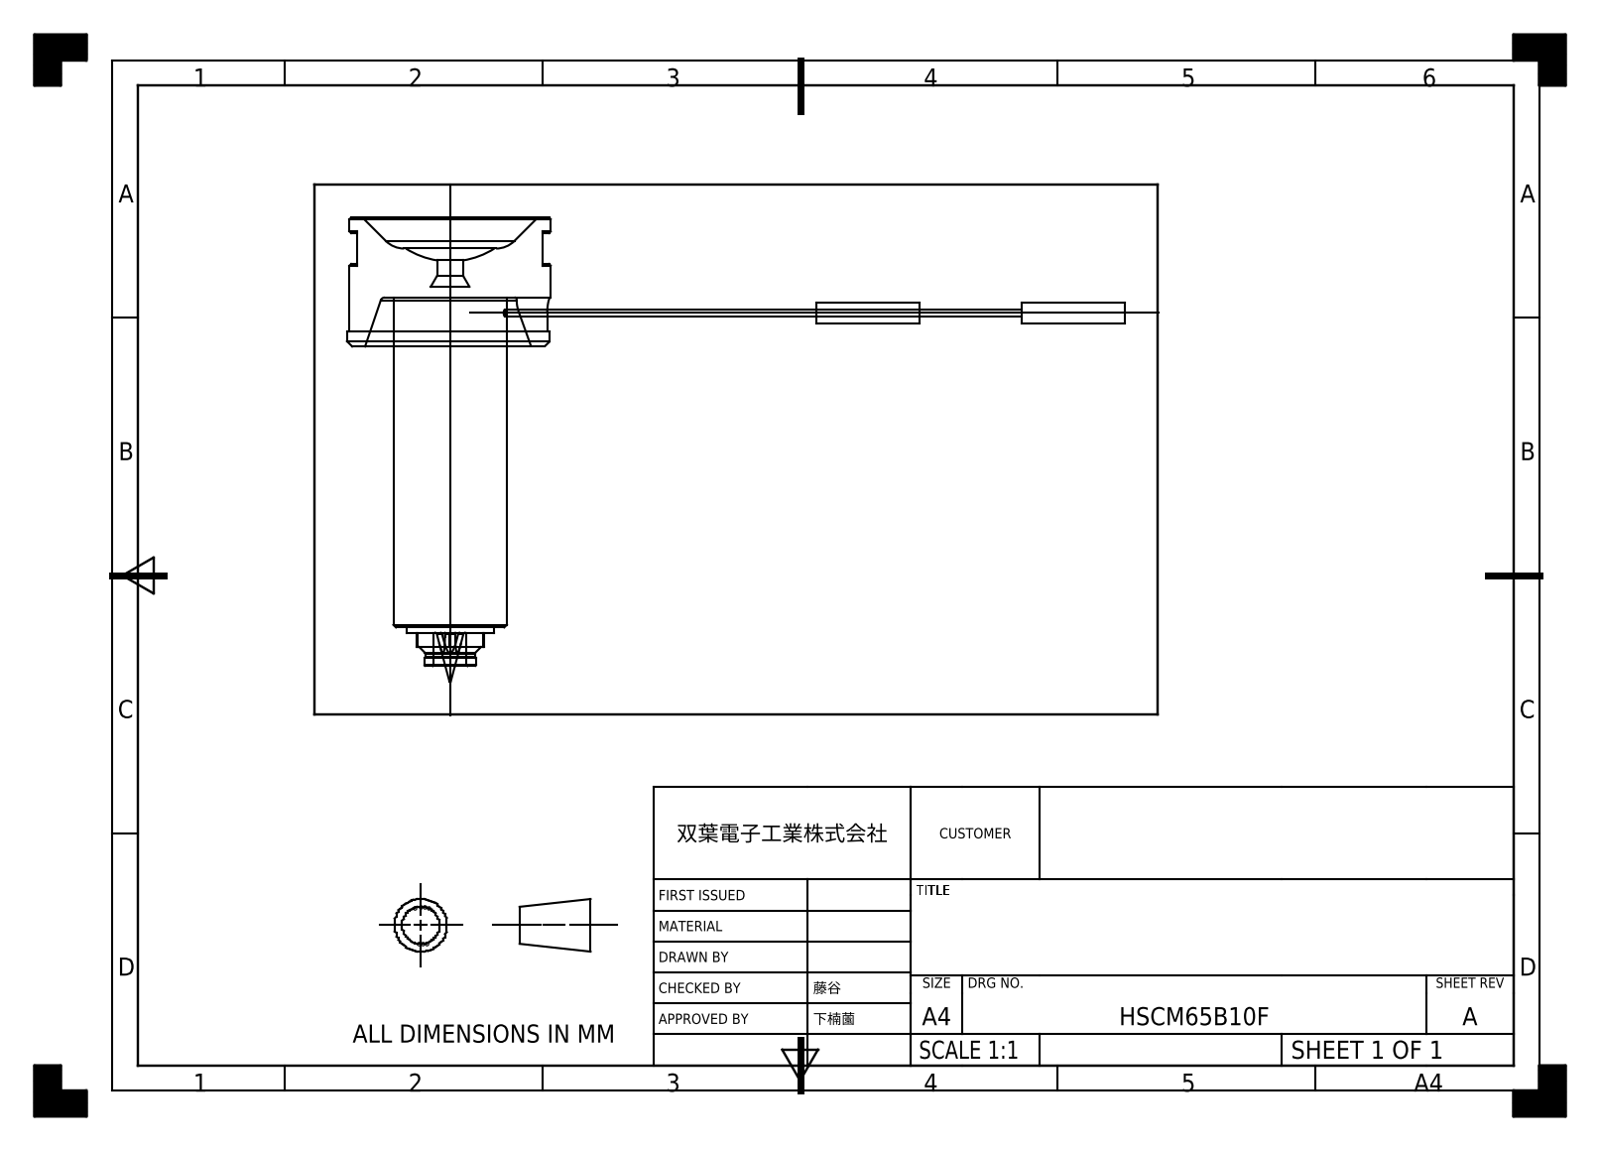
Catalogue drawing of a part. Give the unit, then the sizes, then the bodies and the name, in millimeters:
Units: millimetres
Overall size (bounding box): 151 × 90 × 40
Round holes (diameter × count): ⌀5 ×1, ⌀6.35 ×1
Round bosses / shafts (diameter × count): ⌀4 ×2, ⌀1.2 ×2, ⌀40 ×1, ⌀39 ×1, ⌀22 ×1, ⌀16.9 ×1, ⌀10 ×1, ⌀9.6 ×1
Partial cylindrical surfaces — rounded edges, fillets, slot ends (radius × count): R2.8 ×3, R3 ×2, R7.45 ×1
Main face-to-face distances: 25, 9.5, 15.5, 65, 79.5, 64, 54.5, 3, 6.5, 80.5
Volume: 44 395 mm³ · Surface area: 12 449 mm²
Bodies: 1 solid, 75 faces (30 planar, 23 cylindrical, 22 other)
Part name (STEP PRODUCT): HSCM65B10F
STEP written by: SIEMENS PLM Software NX 2023 (AUTOMOTIVE_DESIGN)
